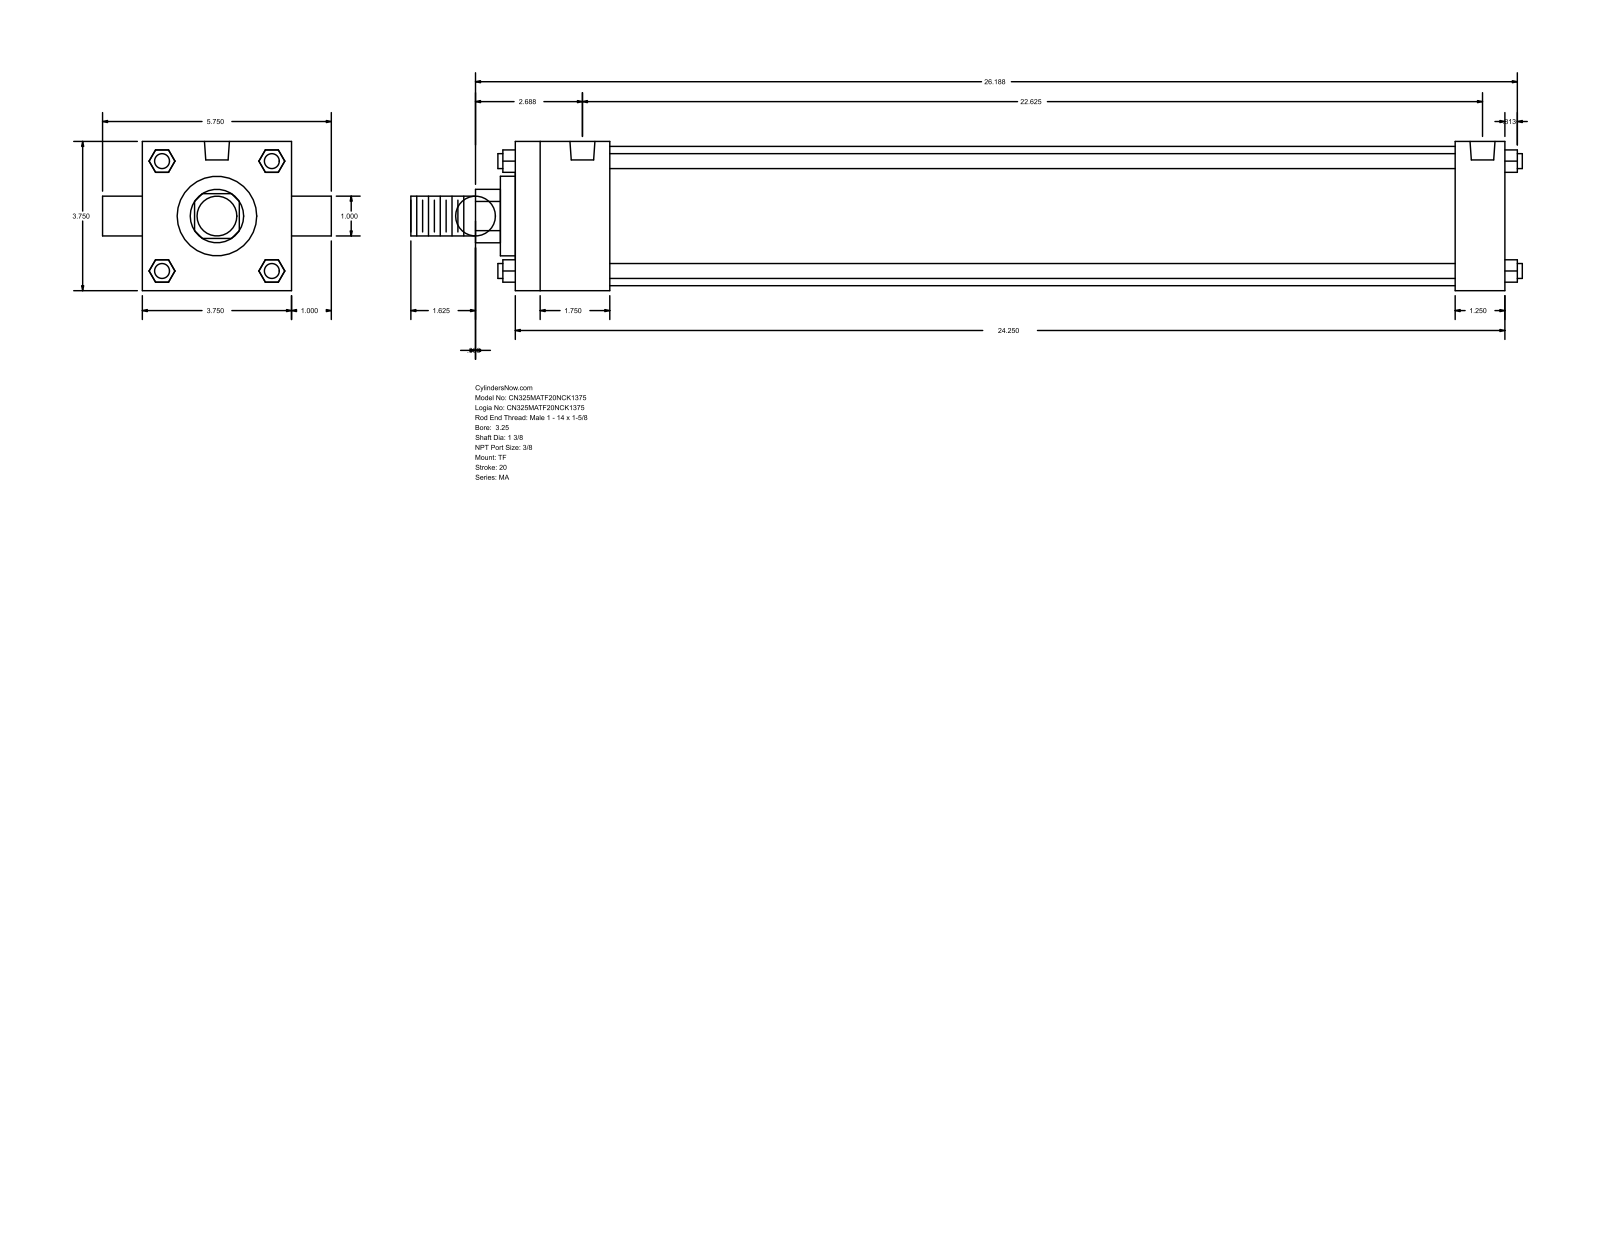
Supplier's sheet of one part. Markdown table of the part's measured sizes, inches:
| quantity | value |
| --- | --- |
| part name | MA_TF__0325_1.375 |
| STEP written by | GSSL Pune (CONFIG_CONTROL_DESIGN) |
| units | inches |
| bodies | 0 solids, 120 faces (92 planar, 28 cylindrical, 0 other) |
| overall size | 27.937 × 5.75 × 3.75 |
| round holes (diameter × count) | 0.437 × 3, 0.627 × 2 |
| round bosses / shafts (diameter × count) | 0.375 × 4, 1 × 2, 3.5 × 1, 2 × 1, 1.375 × 1 |
| partial cylindrical surfaces (radius × count) | 0.672 × 1 |
| main face-to-face distances | 3.75, 24.875, 2.375, 23.625, 21.25, 22.5, 1.25, 0.375, 2.75, 24 |
| hole center spacings | 0.188, 22.437, 22.25, 22.625 |
